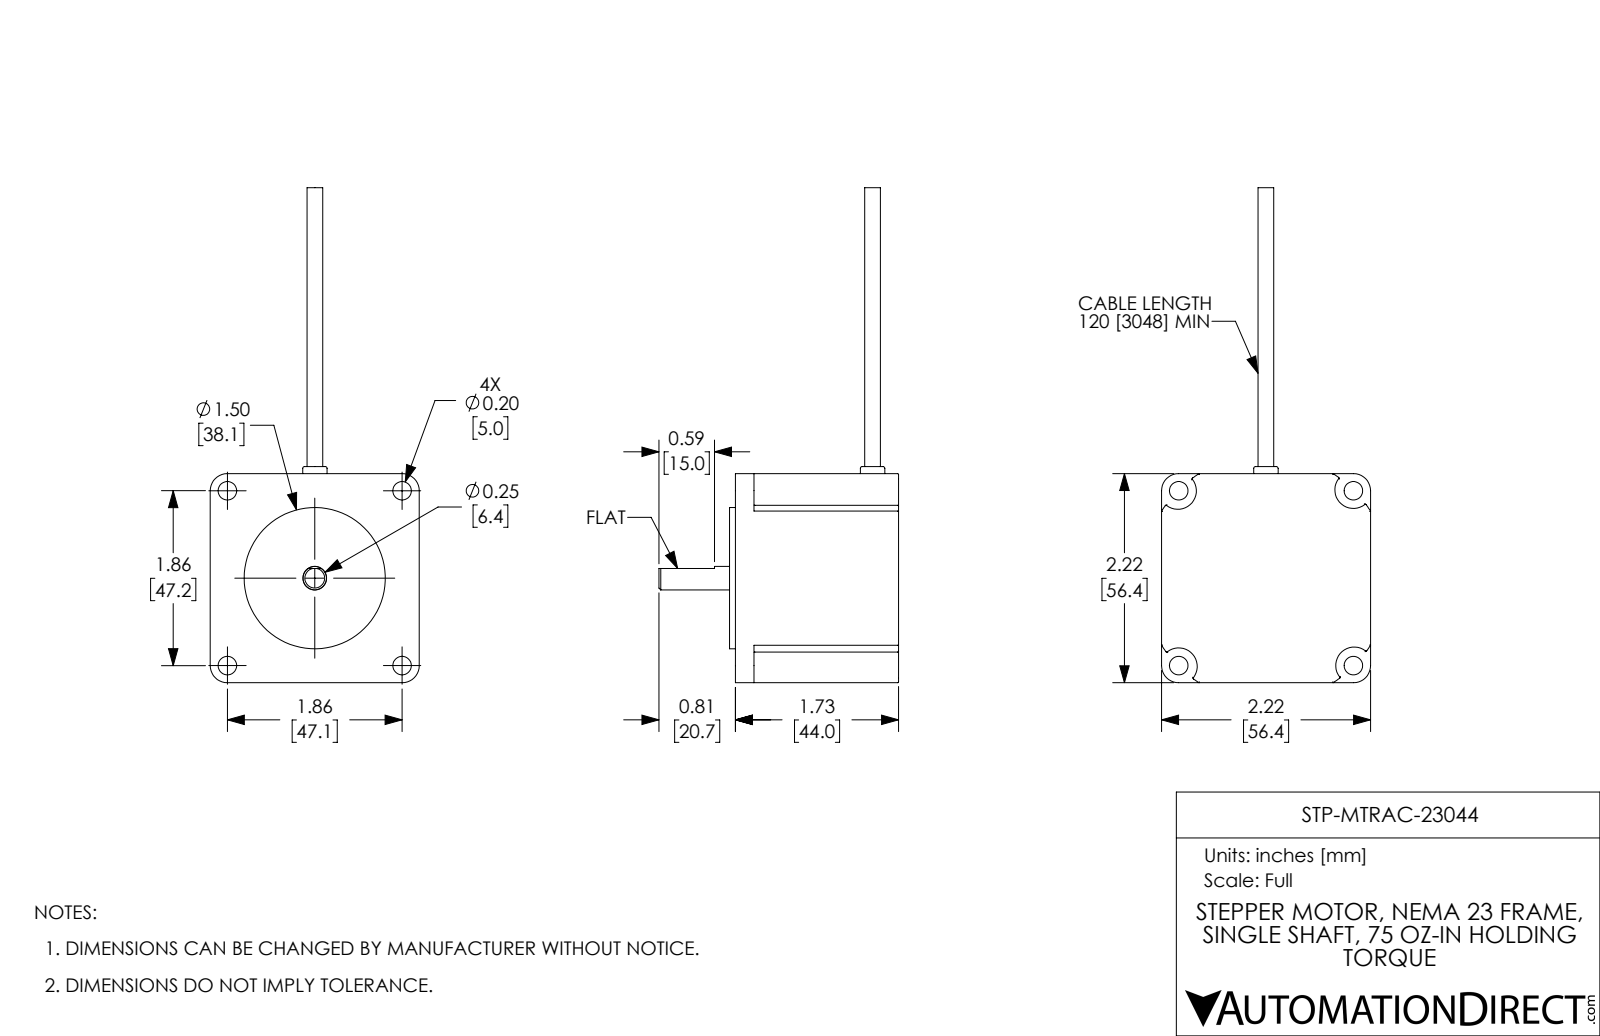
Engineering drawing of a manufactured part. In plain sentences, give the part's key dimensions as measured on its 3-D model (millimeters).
The part is named "STP-MTRAC-23044 from HT23-552-CAA r1". Its 3-D file was written by "SolidWorks 2017 (AUTOMOTIVE_DESIGN)". It is 1 solid with 133 faces: 24 planar, 56 cylindrical and 53 other. Overall it measures 133.5 by 64.6 by 56.4 millimeters. Its volume is 130 200 cubic millimeters and its surface area 17 870 square millimeters. Round holes: 4 of diameter 3, 4 of diameter 5. Round bosses or shafts: 1 of diameter 38.1, 1 of diameter 6.6, 1 of diameter 6.4, 1 of diameter 4.2. Partial cylindrical surfaces (rounded edges, fillets, slot ends): 12 of radius 0.3, 4 of radius 4.6, 4 of radius 5, 1 of radius 33.5. The main face-to-face distances are 56.4, 44, 45.6, 1.6, 5, 39, 6.6, 30.8, 25.6, 4. The hole center spacings are 23.6, 27.4, 40.6, 47.1, 52.2, 13.5, 32.5, 66.7.
